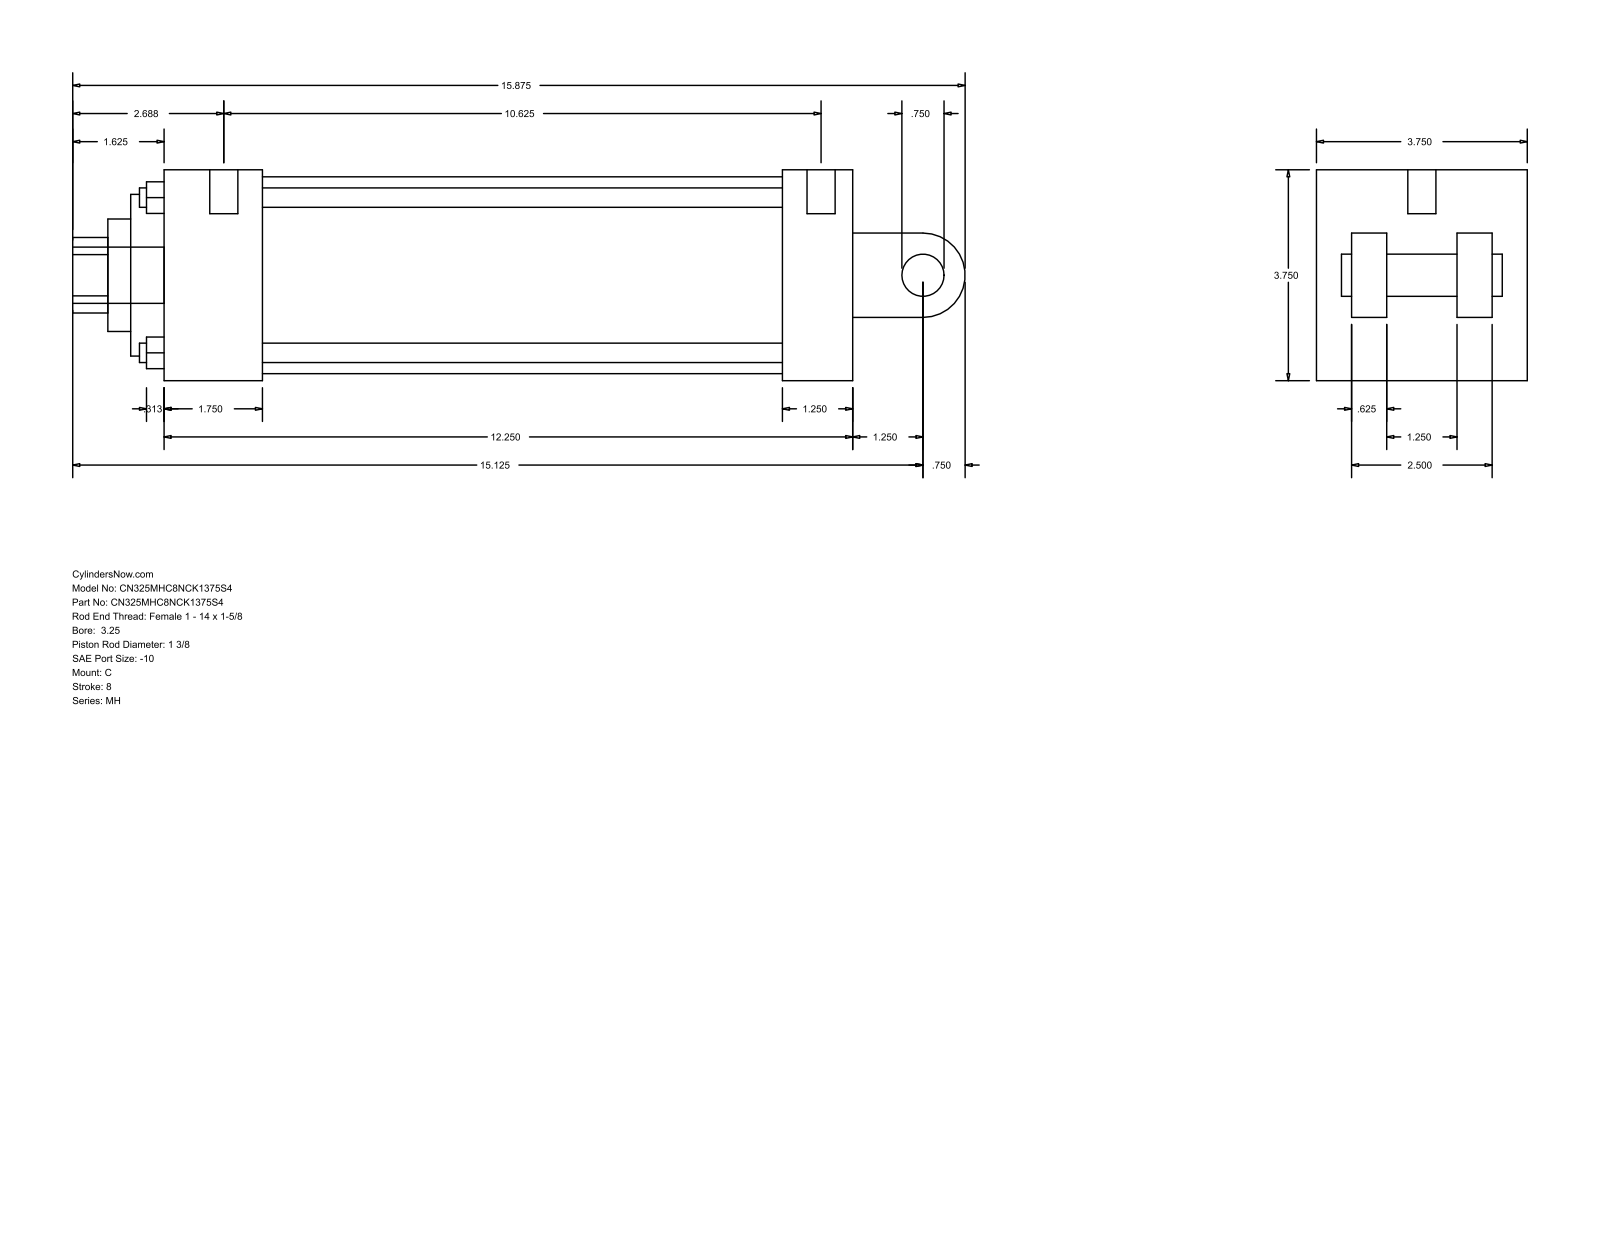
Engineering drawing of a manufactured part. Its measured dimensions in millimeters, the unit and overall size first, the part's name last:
Units: millimetres
Overall size (bounding box): 403.23 × 95.25 × 95.25
Round holes (diameter × count): ⌀8.76 ×4, ⌀5.56 ×2, ⌀12.7 ×1, ⌀34.92 ×1, ⌀50.8 ×1, ⌀73.03 ×1, ⌀88.9 ×1
Round bosses / shafts (diameter × count): ⌀5.56 ×2, ⌀25.4 ×1, ⌀19.05 ×1, ⌀12.7 ×1
Partial cylindrical surfaces — rounded edges, fillets, slot ends (radius × count): R17.06 ×1, R19.05 ×1
Main face-to-face distances: 95.24, 15.87, 311.16, 63.5, 79.37, 31.74, 47.63, 44.45, 279.41, 234.96
Hole centre spacings: 49.57, 70.1, 99.14, 4.76
Bodies: 0 solids, 101 faces (71 planar, 30 cylindrical, 0 other)
Part name (STEP PRODUCT): MH_C__0325_1.375
STEP written by: GSSL Pune (CONFIG_CONTROL_DESIGN)
